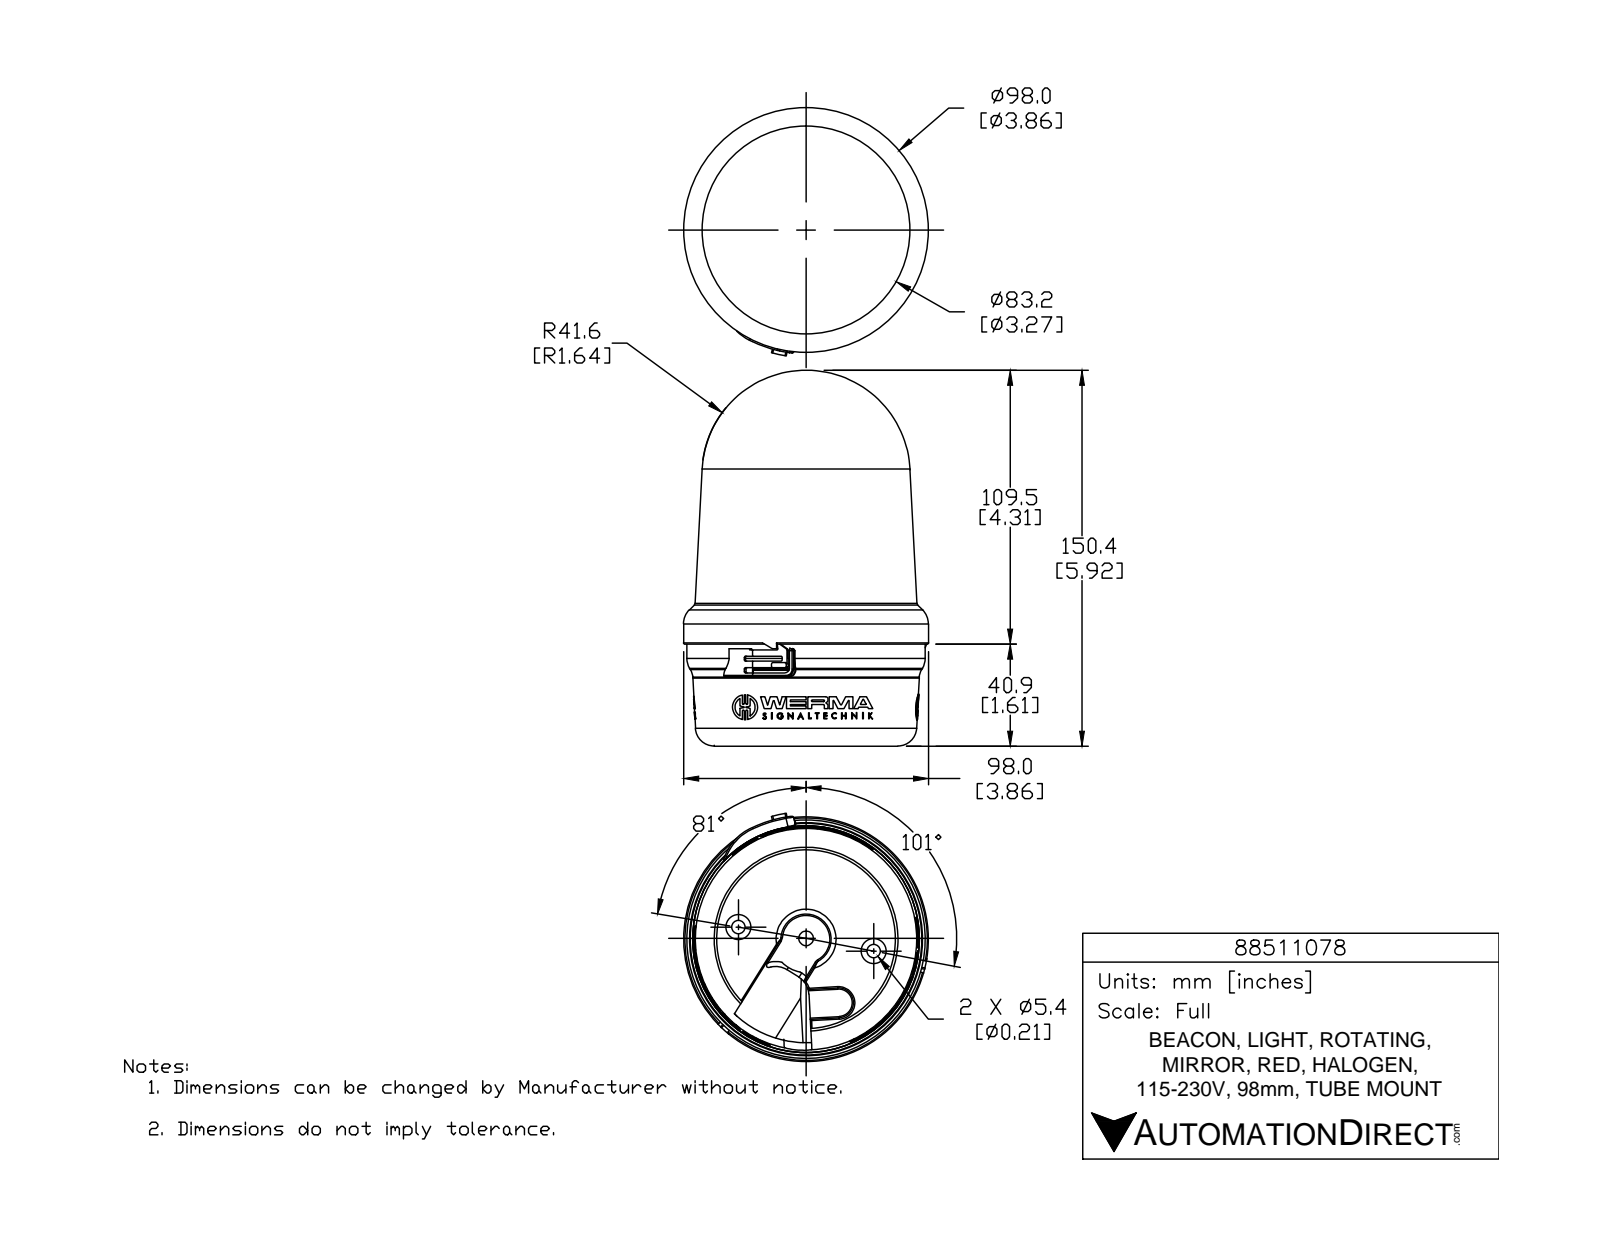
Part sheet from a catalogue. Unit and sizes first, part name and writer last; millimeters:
Units: millimetres
Overall size (bounding box): 201 × 99.4 × 98
Round holes (diameter × count): ⌀2 ×3, ⌀25.7 ×1, ⌀26 ×1
Round bosses / shafts (diameter × count): ⌀11.5 ×3, ⌀2.9 ×3, ⌀98 ×1, ⌀35.8 ×1, ⌀32 ×1
Partial cylindrical surfaces — rounded edges, fillets, slot ends (radius × count): R0.5 ×12, R0.2 ×9, R0.2 ×6, R0.4 ×6, R0.4 ×6, R0.4 ×6, R6.7 ×6, R0.2 ×3
Main face-to-face distances: 56.2, 11.7, 68, 8.5, 3.2, 64.7, 66.1, 62.9, 54.4, 1.9
Volume: 896 400 mm³ · Surface area: 58 960 mm²
Bodies: 1 solid, 1006 faces (554 planar, 189 cylindrical, 263 other)
Part name (STEP PRODUCT): 88511078
STEP written by: SolidWorks 2015 (AUTOMOTIVE_DESIGN)
